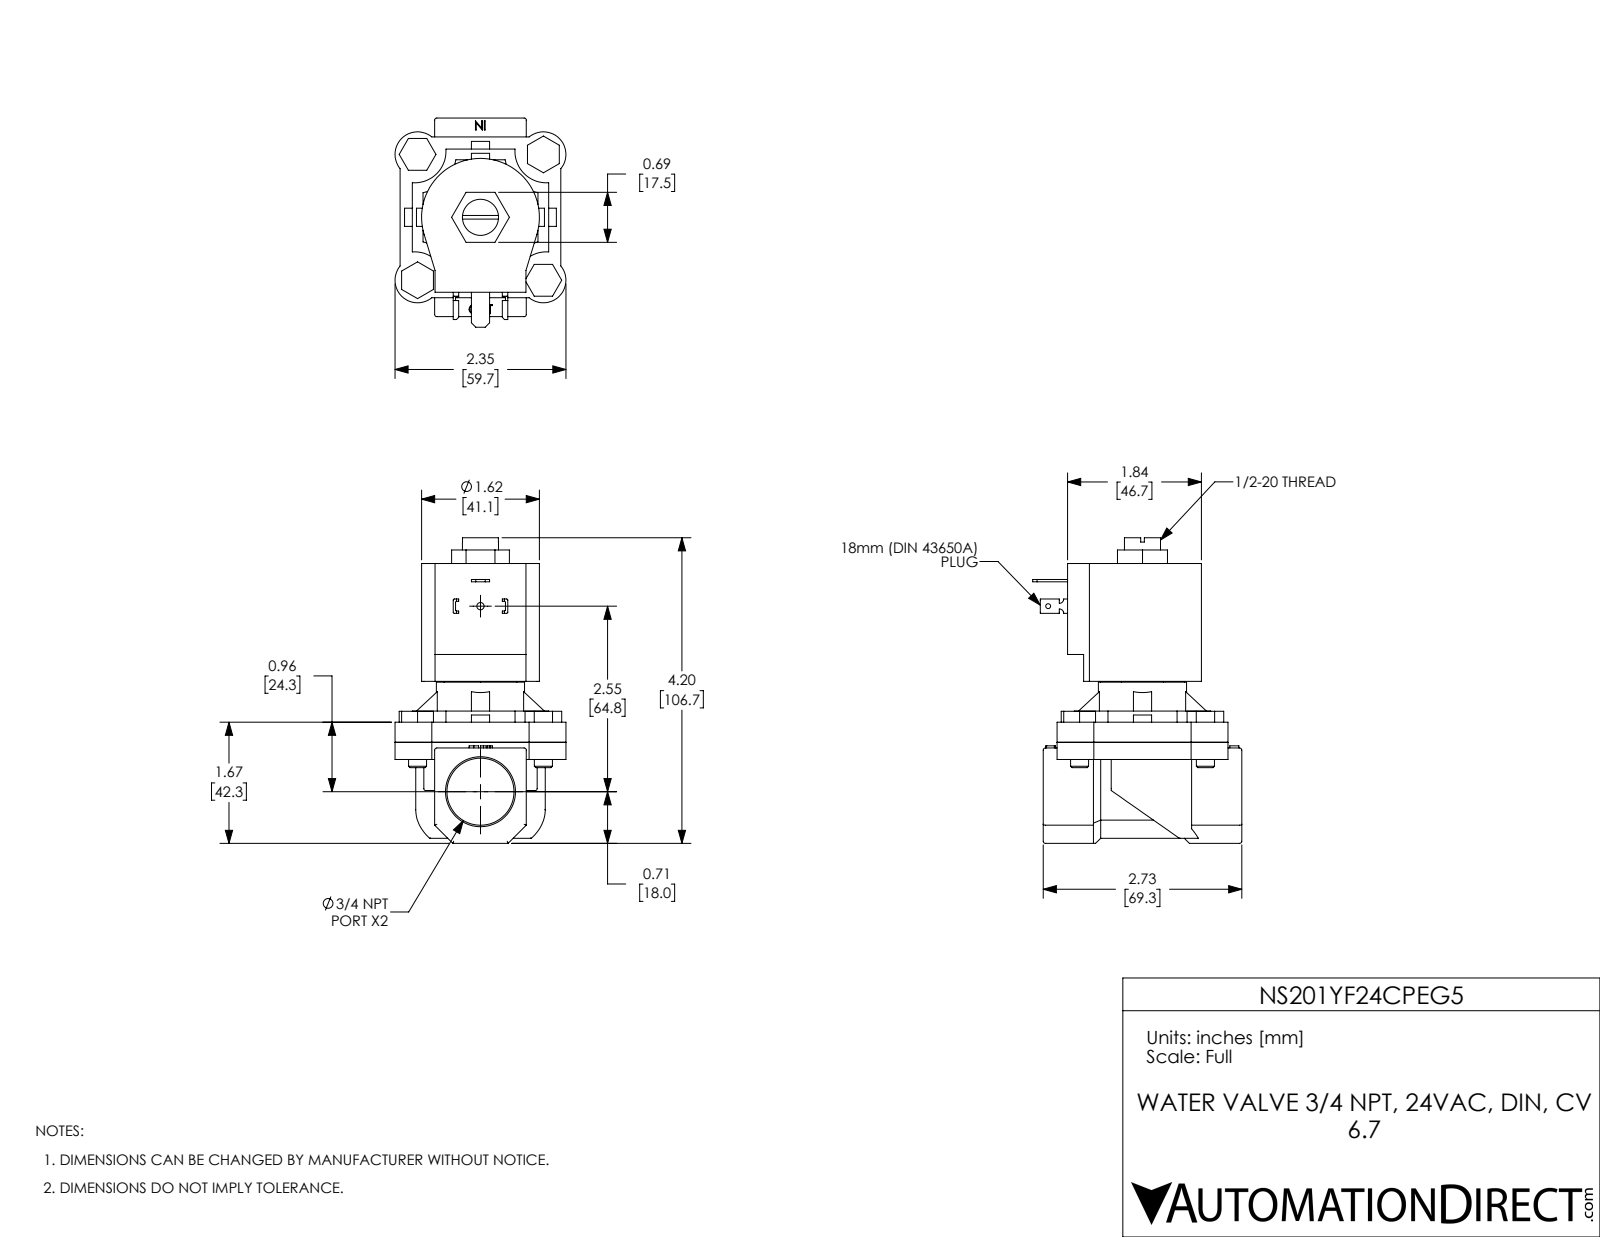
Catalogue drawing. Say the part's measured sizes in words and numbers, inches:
The part is named "NS201YF24CPEG5". Its 3-D file was written by "SolidWorks 2021 (CONFIG_CONTROL_DESIGN)". It is 11 solids with 387 faces: 241 planar, 113 cylindrical and 33 other. Overall it measures 4.2 by 2.875 by 2.35 inches. Its volume is 10.6 cubic inches and its surface area 70.72 square inches. Round holes: 4 of diameter 0.25, 1 of diameter 0.067, 1 of diameter 0.1, 1 of diameter 0.496, 1 of diameter 0.512, 1 of diameter 0.922, 1 of diameter 1.155. Round bosses or shafts: 4 of diameter 0.248, 1 of diameter 1.213. Partial cylindrical surfaces (rounded edges, fillets, slot ends): 15 of radius 0.03, 8 of radius 0.015, 4 of radius 0.31, 4 of radius 0.432, 4 of radius 0.579, 2 of radius 0.06, 1 of radius 0.81, 1 of radius 0.89. The main face-to-face distances are 0.276, 2.457, 2.181, 0.236, 0.512, 2.693, 0.475, 1.735, 1.26, 2.21. The hole center spacings are 1.223, 1.73, 2.446, 2.55.
